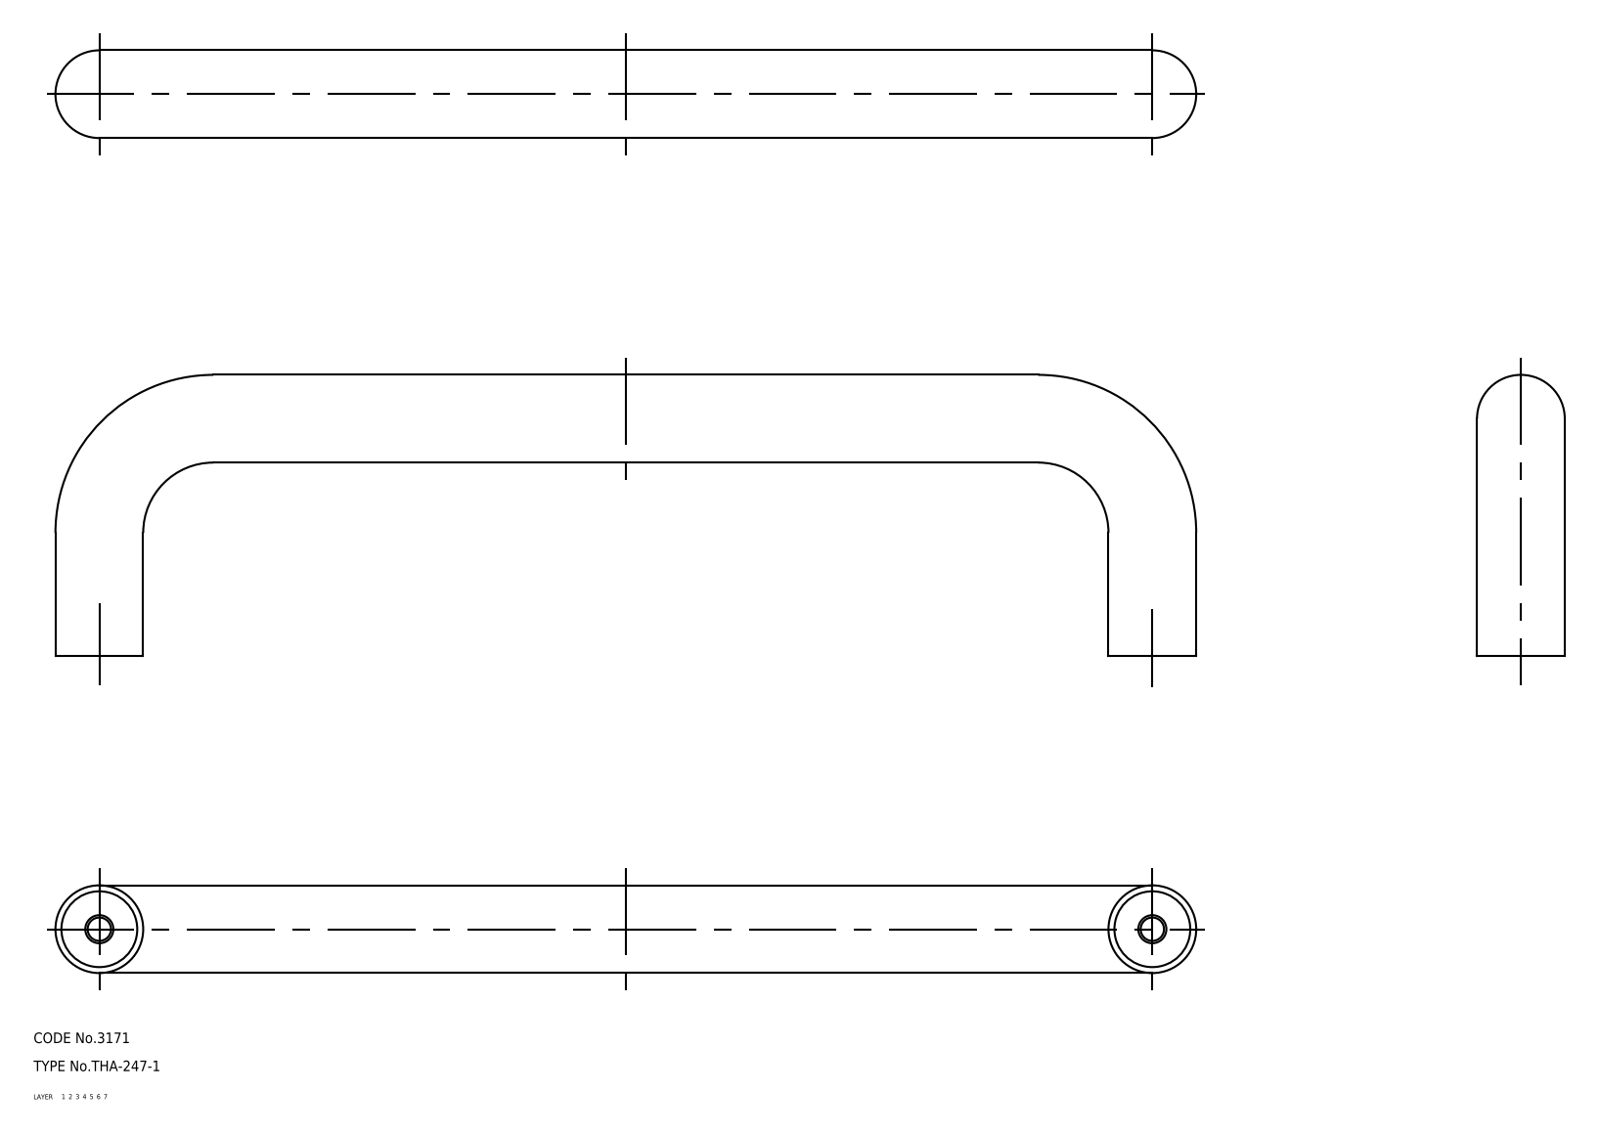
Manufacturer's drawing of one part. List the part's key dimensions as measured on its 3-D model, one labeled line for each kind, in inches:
Part name (STEP PRODUCT): attachment; pull; THA_247_1_28054_36
STEP written by: CADfix (AUTOMOTIVE_DESIGN)
Units: inches
Bodies: 3 solids, 34 faces (0 planar, 0 cylindrical, 34 other)
Overall size (bounding box): 12.795 × 3.15 × 0.984
Volume: 3.739 in³ · Surface area: 99.4 in²
